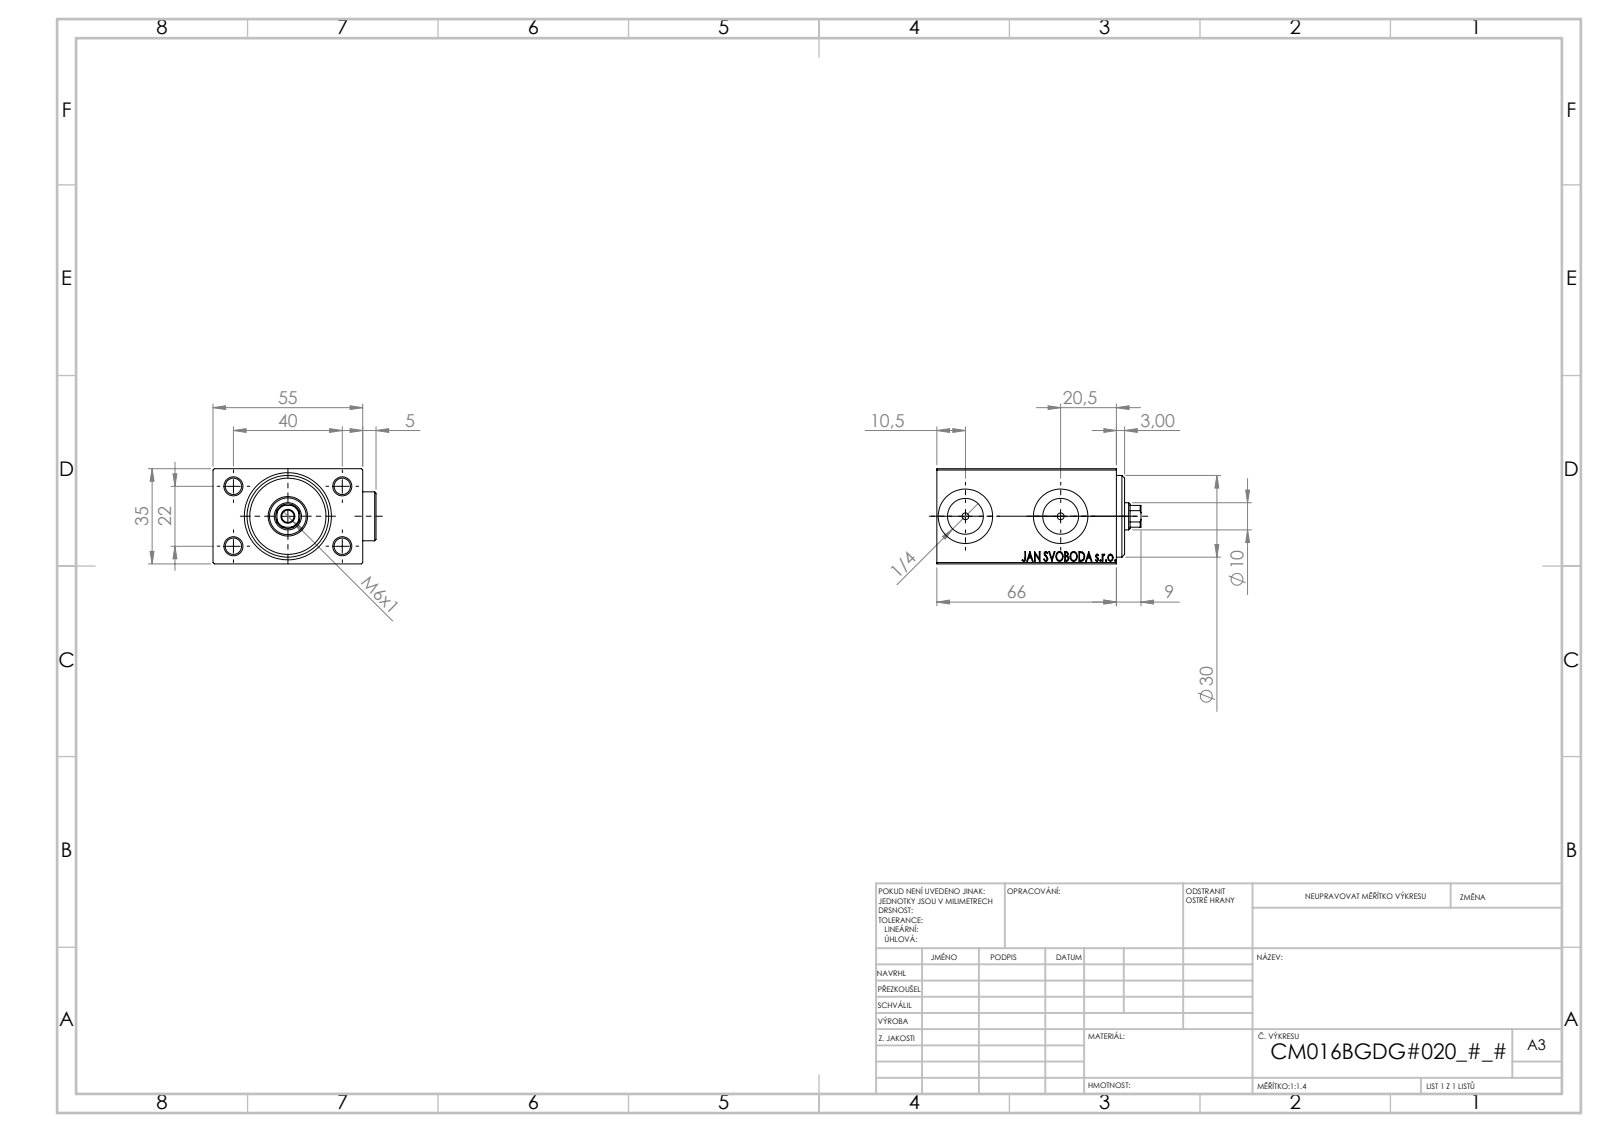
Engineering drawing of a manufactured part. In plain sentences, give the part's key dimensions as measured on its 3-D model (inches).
The part is named "V450CM_VC_B; V450CM_B_Body; Zatka_OIL_PORT; V450CM_B_VCP". Its 3-D file was written by "SolidWorks 2019 (CONFIG_CONTROL_DESIGN)". It is 5 solids with 935 faces: 435 planar, 70 cylindrical and 430 other. Overall it measures 2.953 by 2.358 by 1.378 inches. Its volume is 7.277 cubic inches and its surface area 47.24 square inches. Round holes: 4 of diameter 0.236, 2 of diameter 0.098, 2 of diameter 0.518, 2 of diameter 0.787, 1 of diameter 0.177, 1 of diameter 0.394, 1 of diameter 0.531, 1 of diameter 0.571, 1 of diameter 0.63, 1 of diameter 0.709, 1 of diameter 1.181. Round bosses or shafts: 2 of diameter 0.709. Partial cylindrical surfaces (rounded edges, fillets, slot ends): 1 of radius 0.177. The main face-to-face distances are 1.378, 0.197, 2.165, 2.402, 2.161, 2.598, 0.118, 0.315, 2.717, 2.157. The hole center spacings are 0.899, 0.866, 1.575, 1.797, 1.378.
